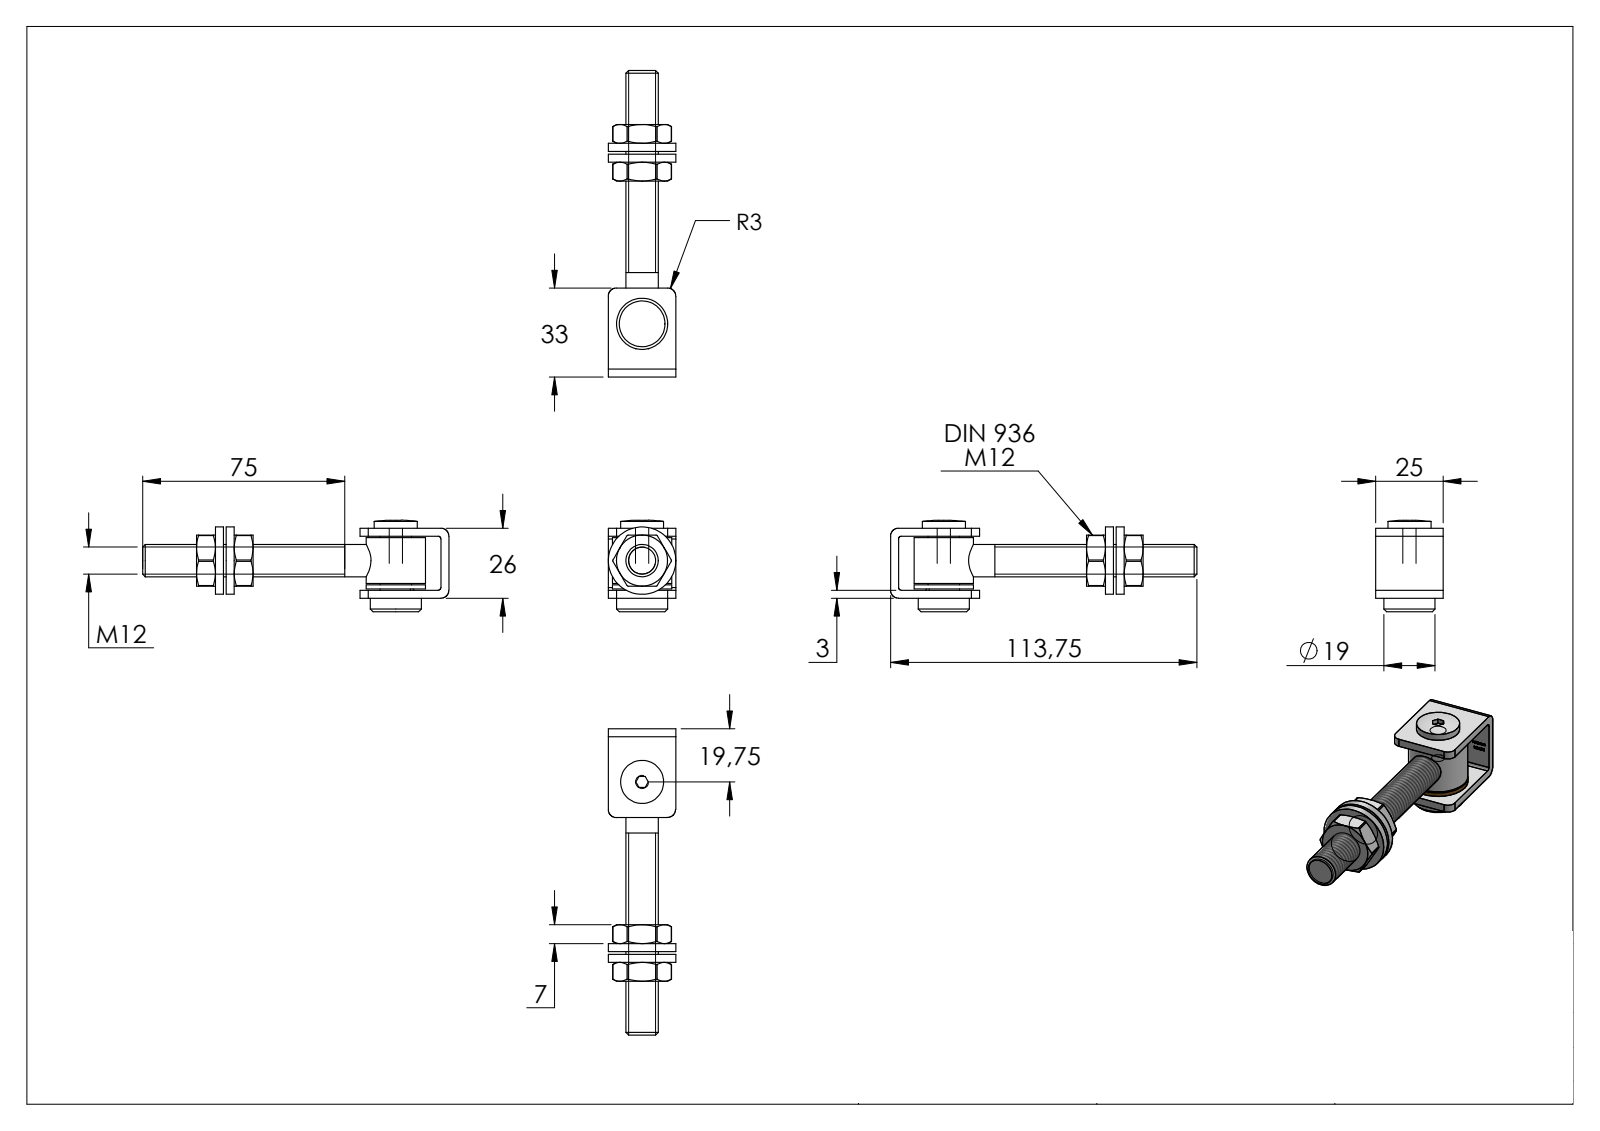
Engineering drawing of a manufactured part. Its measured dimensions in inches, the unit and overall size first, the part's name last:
Units: inches
Overall size (bounding box): 866.142 × 826.772 × 826.772
Round holes (diameter × count): ⌀0.197 ×1, ⌀0.402 ×1, ⌀0.492 ×1, ⌀0.512 ×1
Round bosses / shafts (diameter × count): ⌀0.984 ×1, ⌀0.866 ×1, ⌀0.748 ×1, ⌀0.63 ×1, ⌀0.472 ×1, ⌀0.461 ×1, ⌀0.236 ×1
Partial cylindrical surfaces — rounded edges, fillets, slot ends (radius × count): R0.02 ×6, R0.118 ×4, R0.039 ×2
Main face-to-face distances: 0.118, 0.906, 0.02, 0.276, 3.14, 3.297, 0.787, 1.024, 0.039, 0.157
Volume: 1.814 in³ · Surface area: 27.95 in²
Bodies: 9 solids, 388 faces (189 planar, 56 cylindrical, 143 other)
Part name (STEP PRODUCT): 130-Mxx Teil6; DIN 936 M8-M24; Torband Teil1_130-M12 Teil1; Torband Teil3_130-M12 Teil3 (+8 more)
STEP written by: SolidWorks 2018 (CONFIG_CONTROL_DESIGN)
